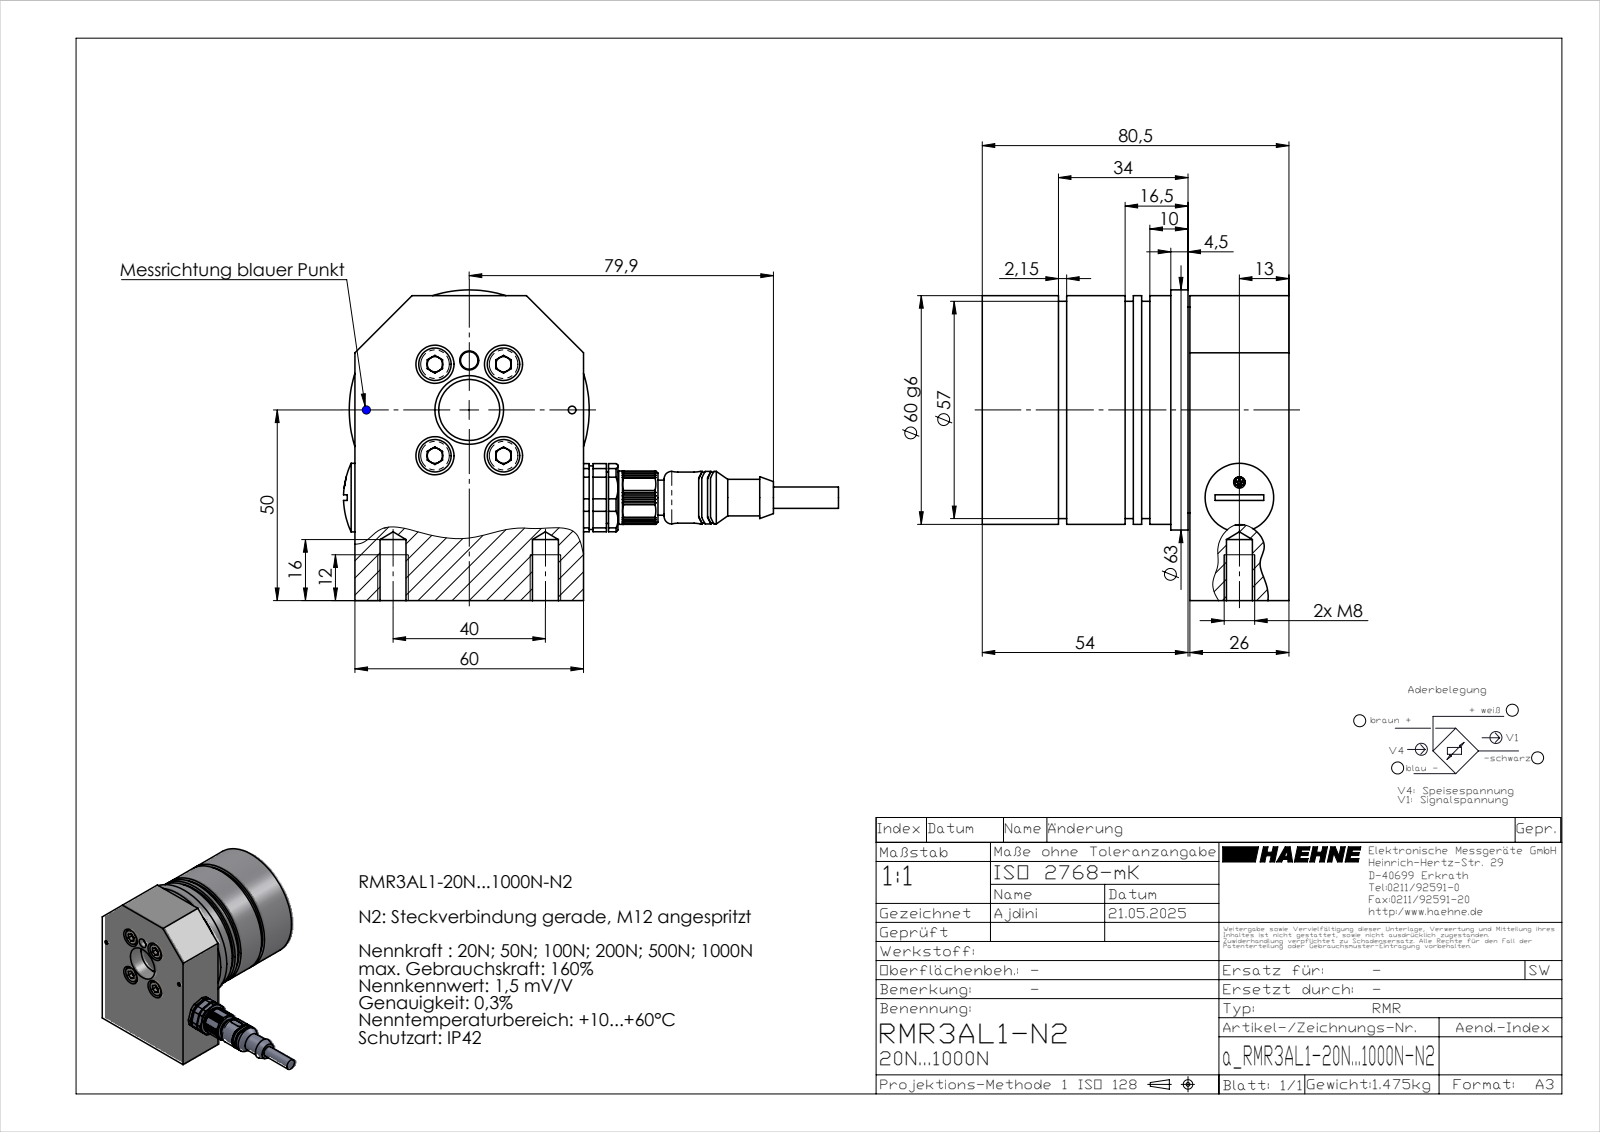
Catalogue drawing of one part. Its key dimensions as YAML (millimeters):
part_name: "a_RMR3AL1-20N...1000N-N2"
step_written_by: "SolidWorks 2023 (AUTOMOTIVE_DESIGN)"
units: millimeters
bodies: {solids: 15, faces: 917, planar: 518, cylindrical: 253, other: 146}
overall_size: [129.92, 81.5, 80.5]
volume: 235095
surface_area: 73304
round_holes:
  - {diameter: 1.1, count: 4}
  - {diameter: 1.15, count: 4}
  - {diameter: 1.6, count: 4}
  - {diameter: 1.85, count: 4}
  - {diameter: 4.2, count: 4}
  - {diameter: 5.3, count: 4}
  - {diameter: 10, count: 4}
  - {diameter: 2, count: 2}
  - {diameter: 6.8, count: 2}
  - {diameter: 0.64, count: 1}
  - {diameter: 1.2, count: 1}
  - {diameter: 3, count: 1}
round_bosses_or_shafts:
  - {diameter: 0.86, count: 5}
  - {diameter: 8.5, count: 4}
  - {diameter: 5, count: 4}
  - {diameter: 1.8, count: 4}
  - {diameter: 1.55, count: 4}
  - {diameter: 1.5, count: 4}
  - {diameter: 1, count: 4}
  - {diameter: 63, count: 1}
partial_cylinders:
  - {radius: 0.2, count: 16}
  - {radius: 0.3, count: 9}
  - {radius: 0.4, count: 4}
  - {radius: 0.53, count: 4}
  - {radius: 1, count: 4}
  - {radius: 1.27, count: 4}
  - {radius: 12, count: 4}
  - {radius: 1.6, count: 2}
face_to_face_distances: [11.5, 48.5, 37, 73, 54.5, 62, 11, 47, 15, 26]
hole_center_spacings: [2.5, 3.54, 15, 21.63, 37.95, 5, 9.06, 18]
